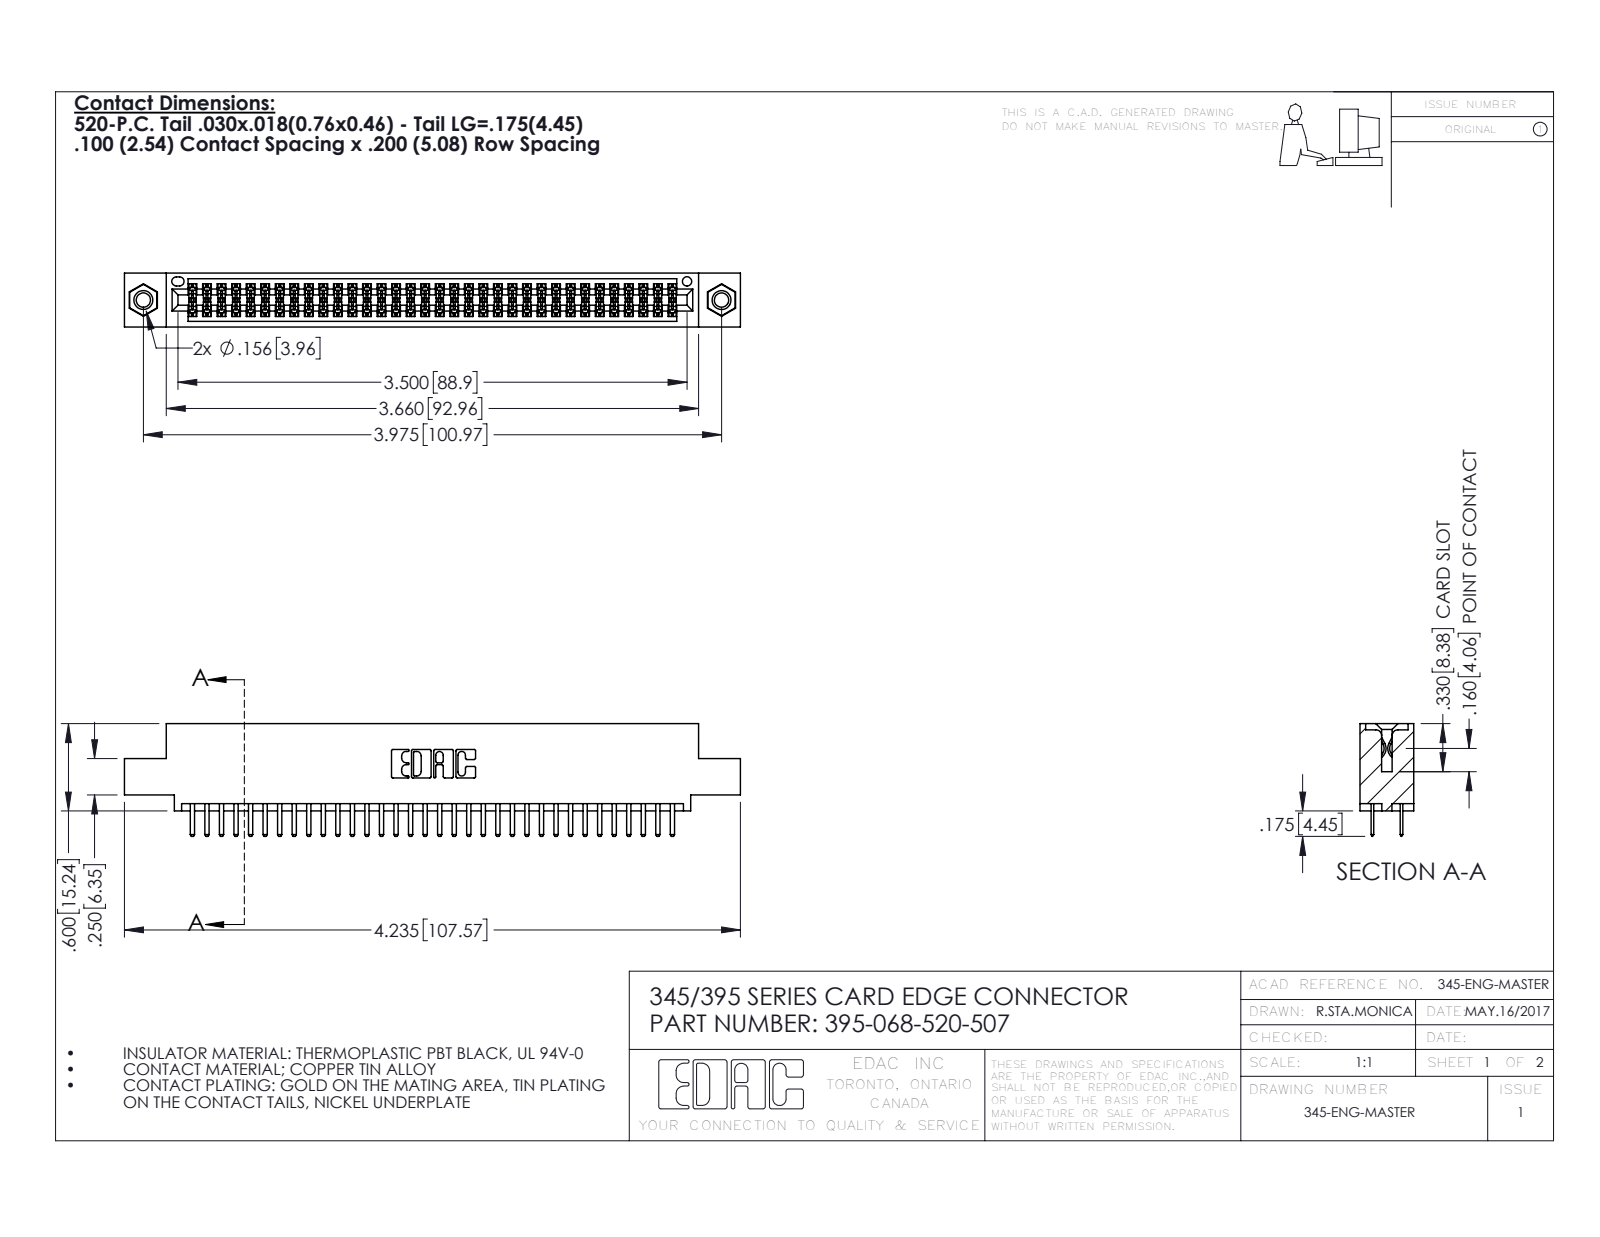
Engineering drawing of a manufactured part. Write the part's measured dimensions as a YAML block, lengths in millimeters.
part_name: "345 Part_0.110 Offset - 0.156 Dia-TI; 345-292-001_345-293-120; 395-068-520-507; 345-250-001_345-250-005-103"
step_written_by: "SolidWorks 2016 (CONFIG_CONTROL_DESIGN)"
units: millimeters
bodies: {solids: 71, faces: 3862, planar: 2496, cylindrical: 1350, other: 16}
overall_size: [107.6, 19.7, 9.4]
volume: 10300
surface_area: 15060
round_holes:
  - {diameter: 2.5, count: 2}
  - {diameter: 3.2, count: 2}
  - {diameter: 4, count: 2}
  - {diameter: 1.6, count: 1}
round_bosses_or_shafts:
  - {diameter: 3.9, count: 2}
partial_cylinders:
  - {radius: 0.2, count: 102}
  - {radius: 0.3, count: 72}
  - {radius: 0.3, count: 22}
  - {radius: 0.2, count: 6}
  - {radius: 0.8, count: 6}
  - {radius: 0.7, count: 3}
  - {radius: 0.4, count: 2}
  - {radius: 0.5, count: 2}
face_to_face_distances: [1.8, 7.6, 5.1, 9.4, 2.5, 6.9, 0.6, 5.7, 0.6, 1.8]
hole_center_spacings: [6.9, 95, 101]
